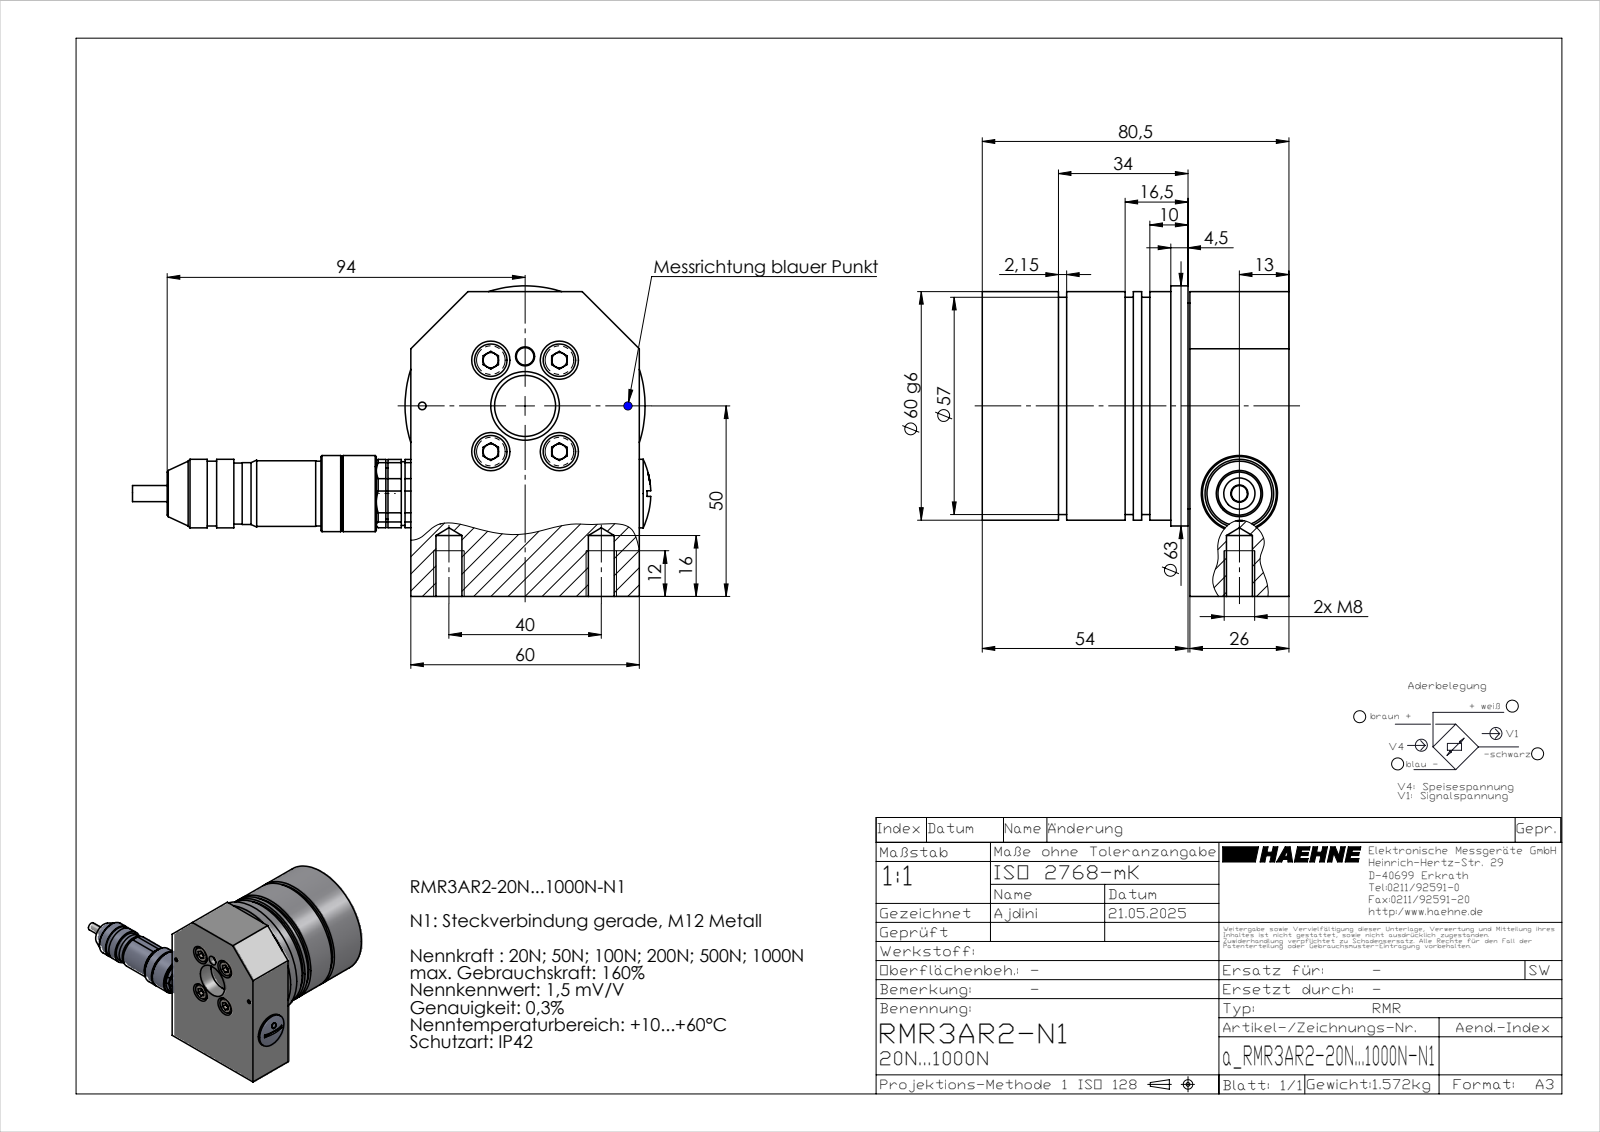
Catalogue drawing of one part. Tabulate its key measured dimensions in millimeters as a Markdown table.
| quantity | value |
| --- | --- |
| part name | a_RMR3AR2-20N...1000N-N1 |
| STEP written by | SolidWorks 2023 (AUTOMOTIVE_DESIGN) |
| units | millimeters |
| bodies | 16 solids, 491 faces (248 planar, 156 cylindrical, 87 other) |
| overall size | 136.04 × 81.5 × 80.5 |
| volume | 243 343 mm³ |
| surface area | 74 838 mm² |
| round holes (diameter × count) | 1 × 5, 4.2 × 4, 5.3 × 4, 10 × 4, 2 × 2, 6.8 × 2, 0.64 × 1, 3 × 1, 4.5 × 1, 5 × 1, 8.2 × 1, 8.37 × 1 |
| round bosses / shafts (diameter × count) | 0.86 × 5, 8.5 × 4, 5 × 4, 1.5 × 4, 1 × 4, 63 × 1, 60 × 1, 57 × 1 |
| partial cylindrical surfaces (radius × count) | 0.3 × 6, 1 × 4, 0.57 × 1, 0.6 × 1, 0.77 × 1, 3.5 × 1, 24 × 1, 40 × 1 |
| main face-to-face distances | 11.5, 48.5, 37, 73, 54.5, 62, 11, 47, 15, 26 |
| hole center spacings | 2.5, 3.54, 15, 21.63, 37.95, 5, 9.06, 18 |
